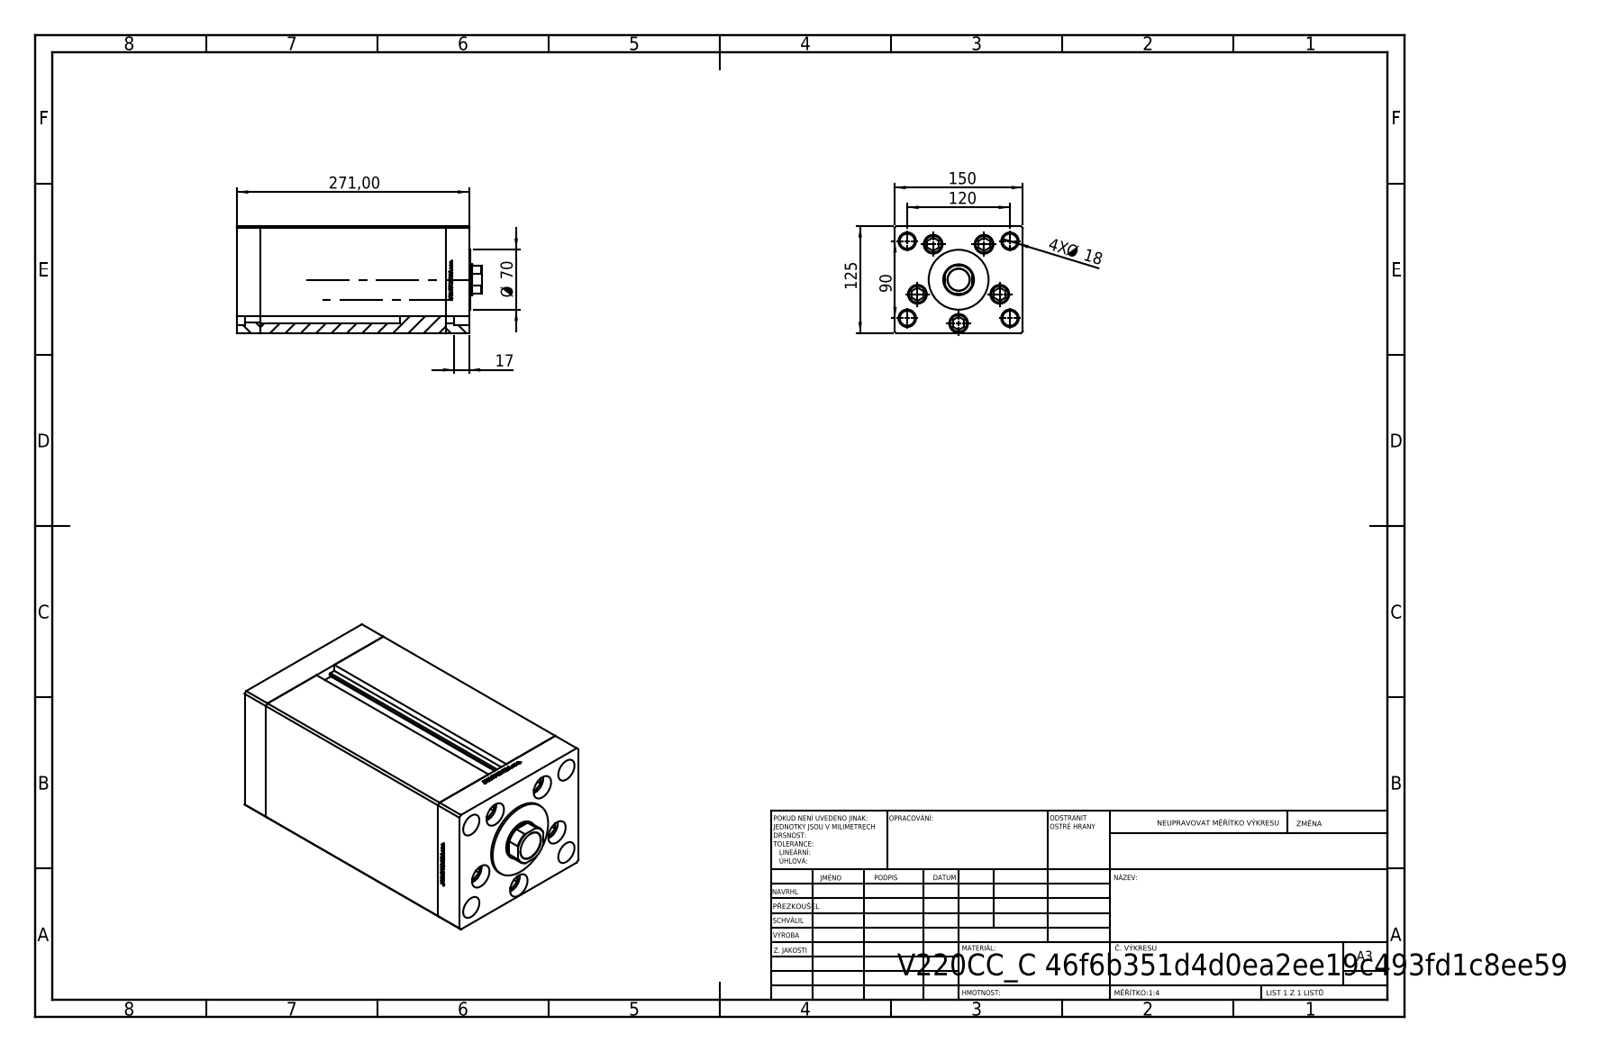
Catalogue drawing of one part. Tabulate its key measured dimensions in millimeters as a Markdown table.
| quantity | value |
| --- | --- |
| part name | ALLEN BOLT; V220C FRONT; V220C_VC_C; V220C BACK_C (+1 more) |
| STEP written by | SolidWorks 2019 (CONFIG_CONTROL_DESIGN) |
| units | millimeters |
| bodies | 13 solids, 1163 faces (542 planar, 159 cylindrical, 462 other) |
| overall size | 286 × 150 × 125 |
| volume | 4 127 000 mm³ |
| surface area | 449 865 mm² |
| round holes (diameter × count) | 17.5 × 9, 22 × 5, 16 × 4, 20.5 × 4, 21 × 1, 25.5 × 1, 36 × 1 |
| round bosses / shafts (diameter × count) | 8 × 5, 21 × 4, 80 × 1, 70 × 1 |
| partial cylindrical surfaces (radius × count) | 0.93 × 2, 17.5 × 1 |
| main face-to-face distances | 150, 125, 27, 244, 217, 33.5, 6.5, 271, 237.5, 210.5 |
| hole center spacings | 51, 75, 30.43, 30.48, 58.89, 60.3, 61.25, 63.14 |
